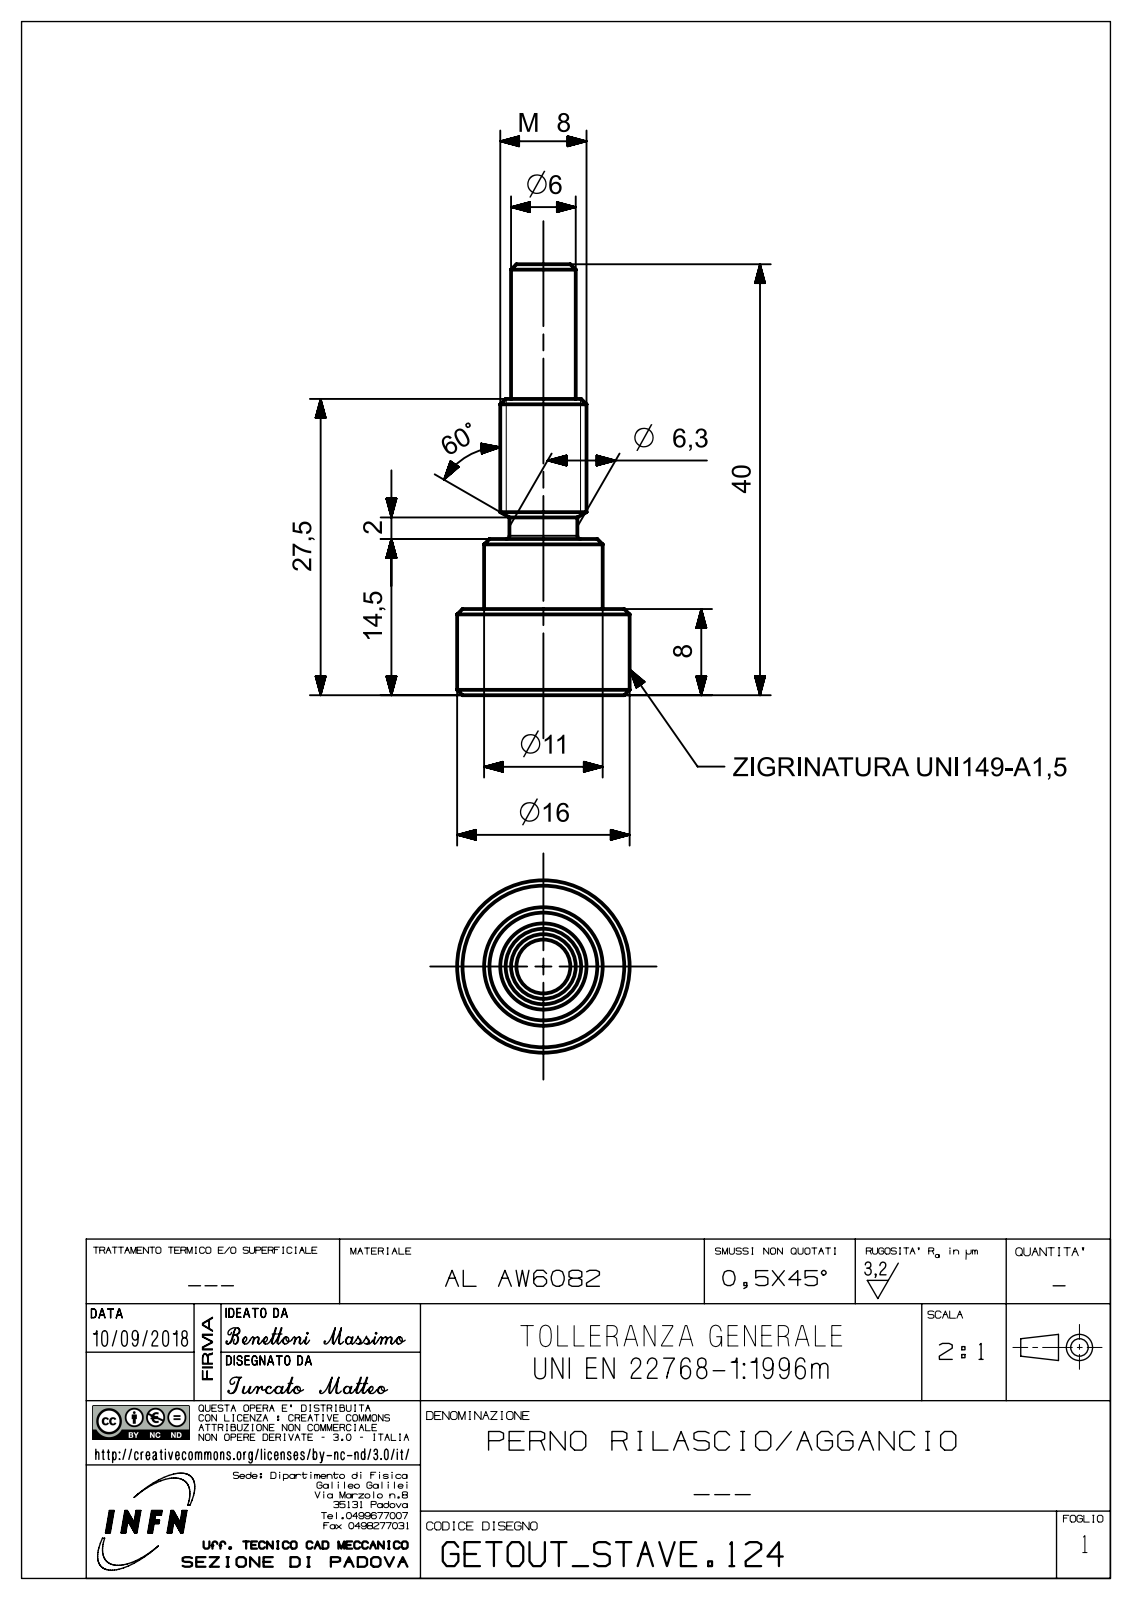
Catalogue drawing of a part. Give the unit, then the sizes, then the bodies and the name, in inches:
Units: inches
Overall size (bounding box): 1.575 × 0.63 × 0.63
Round bosses / shafts (diameter × count): ⌀0.63 ×1, ⌀0.433 ×1, ⌀0.315 ×1, ⌀0.248 ×1, ⌀0.236 ×1
Main face-to-face distances: 0.315, 0.571, 0.256, 1.575, 1.26, 1.004, 1.083, 0.768, 0.512, 0.492
Volume: 0.193 in³ · Surface area: 2.407 in²
Bodies: 1 solid, 17 faces (5 planar, 5 cylindrical, 7 other)
Part name (STEP PRODUCT): bezA730AE56cd2z
STEP written by: SIEMENS PLM Software NX 12.0 (AUTOMOTIVE_DESIGN)
